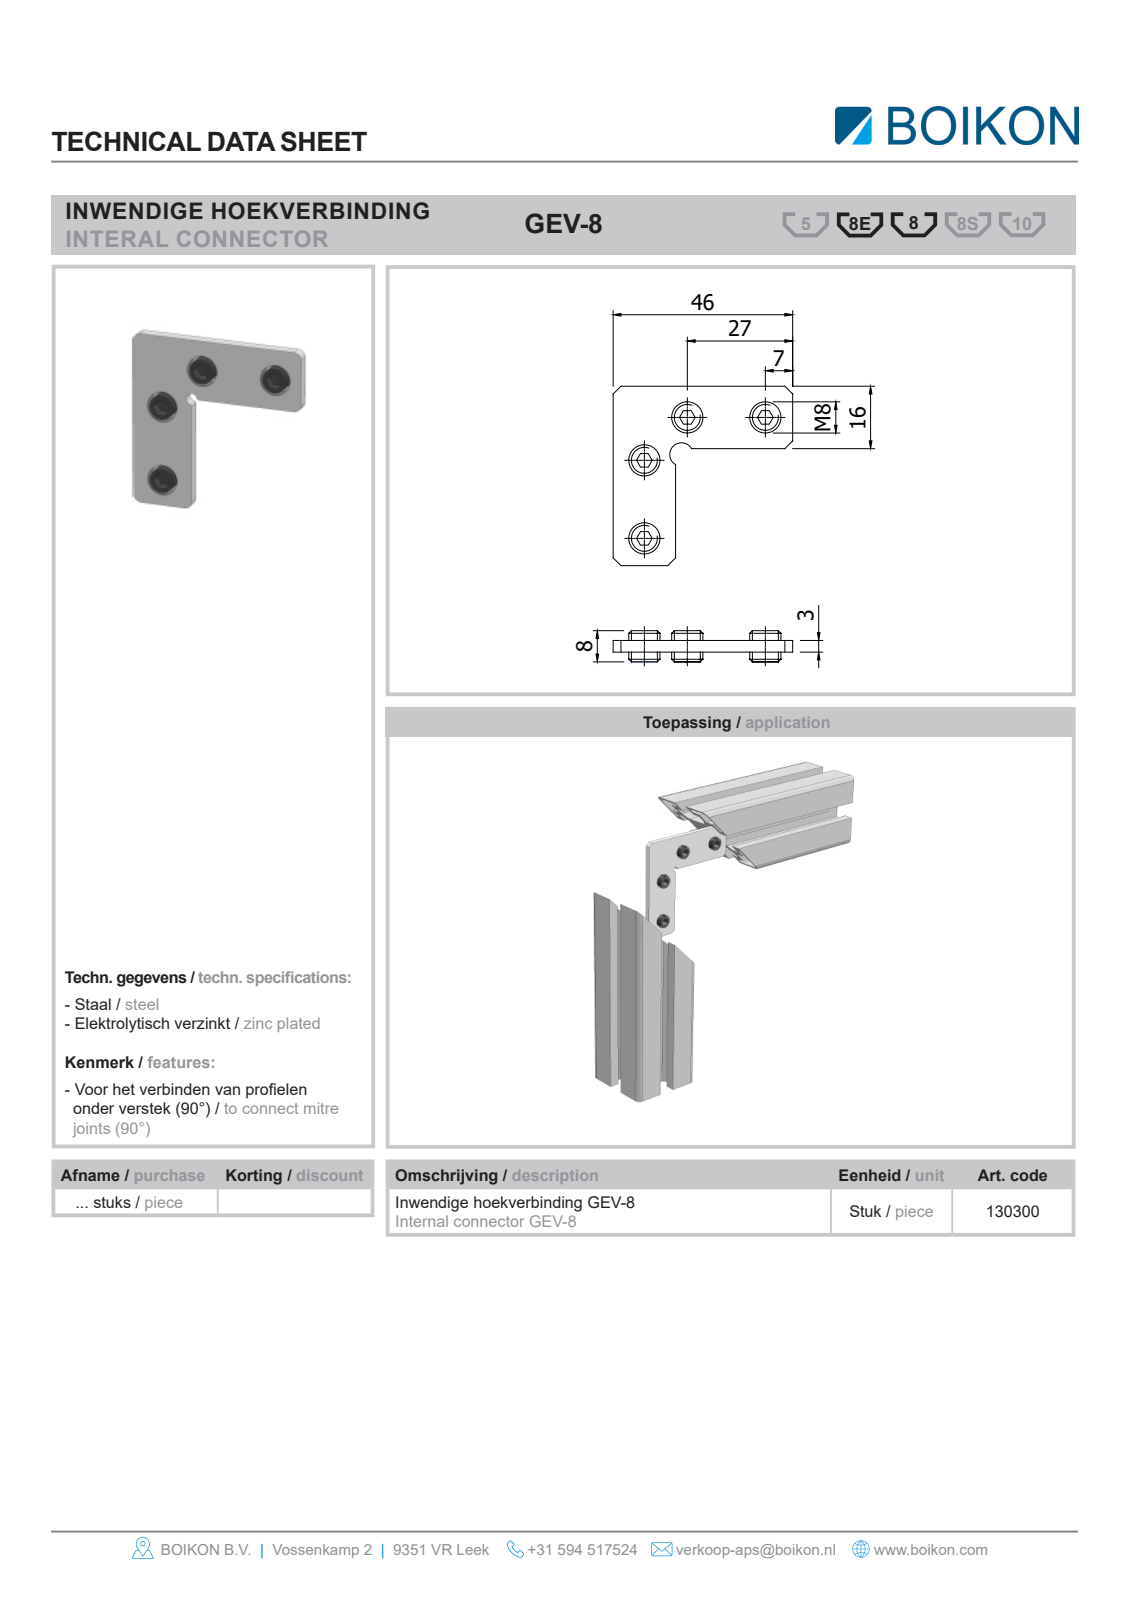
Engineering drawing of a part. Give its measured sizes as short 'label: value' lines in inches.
name: Root; 130300Inwendige hoekverbinding GEV-8BOIKON; DIN EN ISO 4029-M8x8-45HSet screws0
written by: HiCAD 2013 1802.4 Build 509 (AUTOMOTIVE_DESIGN)
unit: in
bodies: 5 solids, 60 faces (44 planar, 8 cylindrical, 8 other)
size: 2.283 × 2.283 × 0.642
volume: 0.236 in³; area: 6.126 in²
holes: 4× ⌀0.315
bosses: 4× ⌀0.255
face distances: 0.118, 0.63, 0.157, 0.039, 1.181, 1.811, 0.079, 0.394, 0.236, 0.682
hole spacings: 0.787, 1.295, 0.613, 1.726
